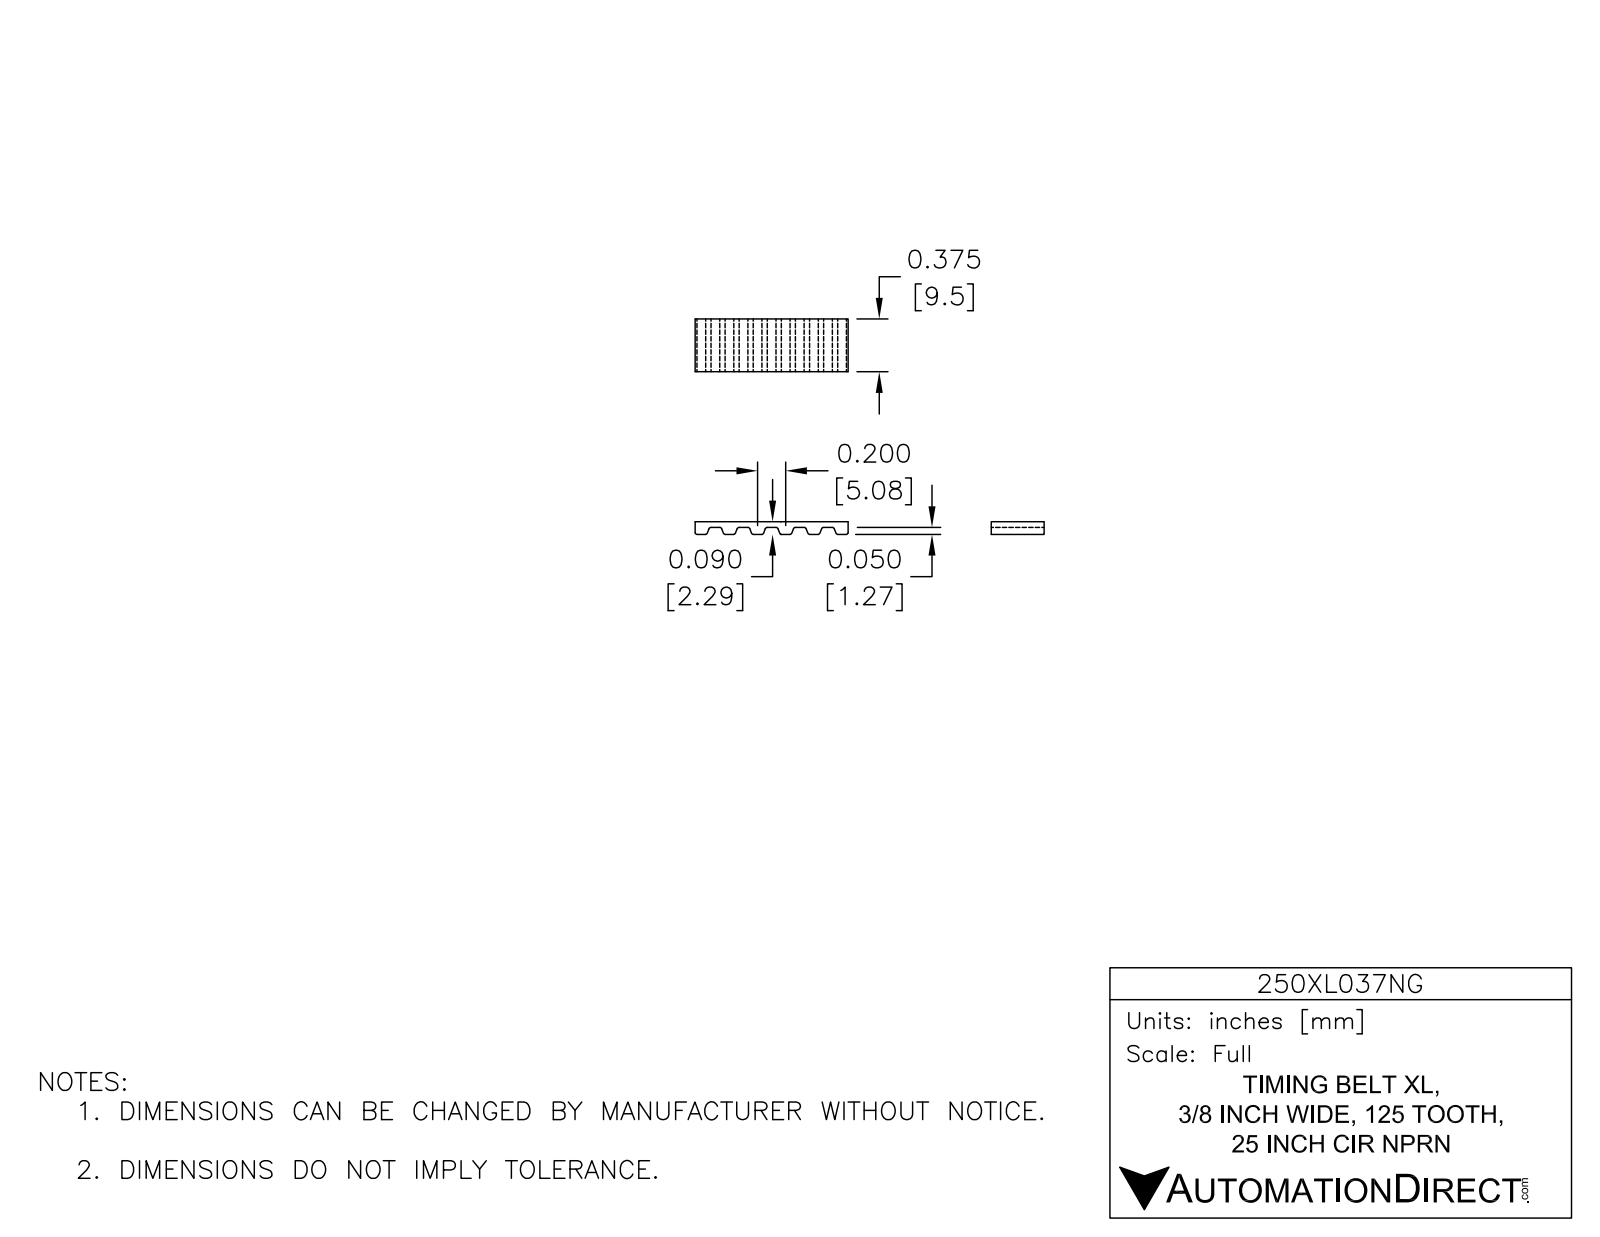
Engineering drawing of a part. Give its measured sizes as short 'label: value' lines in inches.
name: 250XL037NG
written by: SolidWorks 2014 (AUTOMOTIVE_DESIGN)
unit: in
bodies: 1 solid, 1039 faces (458 planar, 581 cylindrical, 0 other)
size: 10.788 × 3 × 0.375
volume: 0.51 in³; area: 23.97 in²
rounds: 500× R0.015, 2× R1.46, 2× R1.5
face distances: 3, 0.04, 2.96, 2.92, 0.375, 0.09, 2.91, 0.05, 2.87, 0.359
